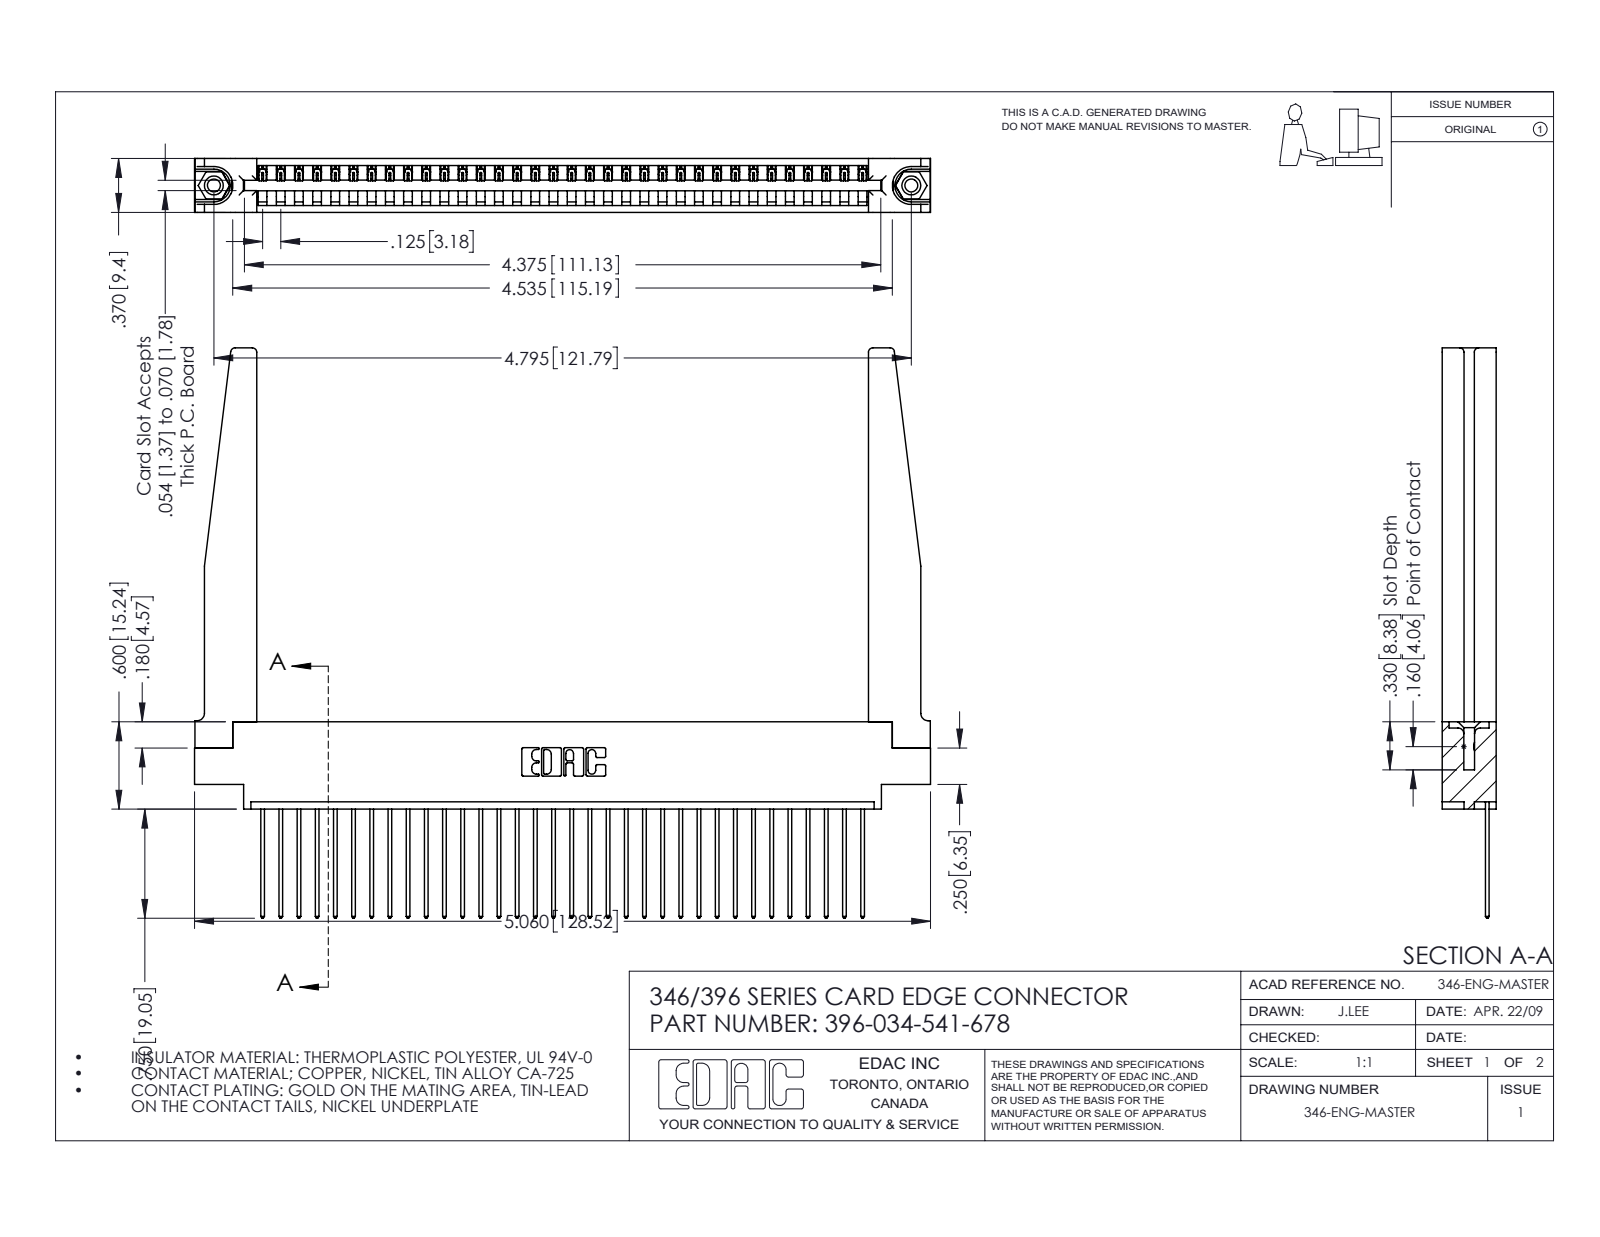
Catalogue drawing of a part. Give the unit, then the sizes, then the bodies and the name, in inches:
Units: inches
Overall size (bounding box): 5.06 × 3.92 × 0.37
Round holes (diameter × count): ⌀0.089 ×2, ⌀0.125 ×2, ⌀0.156 ×2, ⌀0.064 ×1
Round bosses / shafts (diameter × count): ⌀0.155 ×2
Partial cylindrical surfaces — rounded edges, fillets, slot ends (radius × count): R0.006 ×68, R0.01 ×68, R0.01 ×22, R0.03 ×8, R0.007 ×6, R0.031 ×6, R0.026 ×3, R0.031 ×2
Main face-to-face distances: 0.37, 0.048, 0.322, 0.072, 0.148, 0.15, 0.25, 0.298, 0.025, 0.222
Hole centre spacings: 0.246, 4.587, 4.795
Volume: 1.166 in³ · Surface area: 34.94 in²
Bodies: 39 solids, 2332 faces (1582 planar, 698 cylindrical, 52 other)
Part name (STEP PRODUCT): 346 Part_0.170 Offset - 0.156 Dia-TH; 345-250-001_345-250-001-102; 345-292-001_345-293-141; 396-034-541-678 (+1 more)
STEP written by: SolidWorks 2016 (CONFIG_CONTROL_DESIGN)
